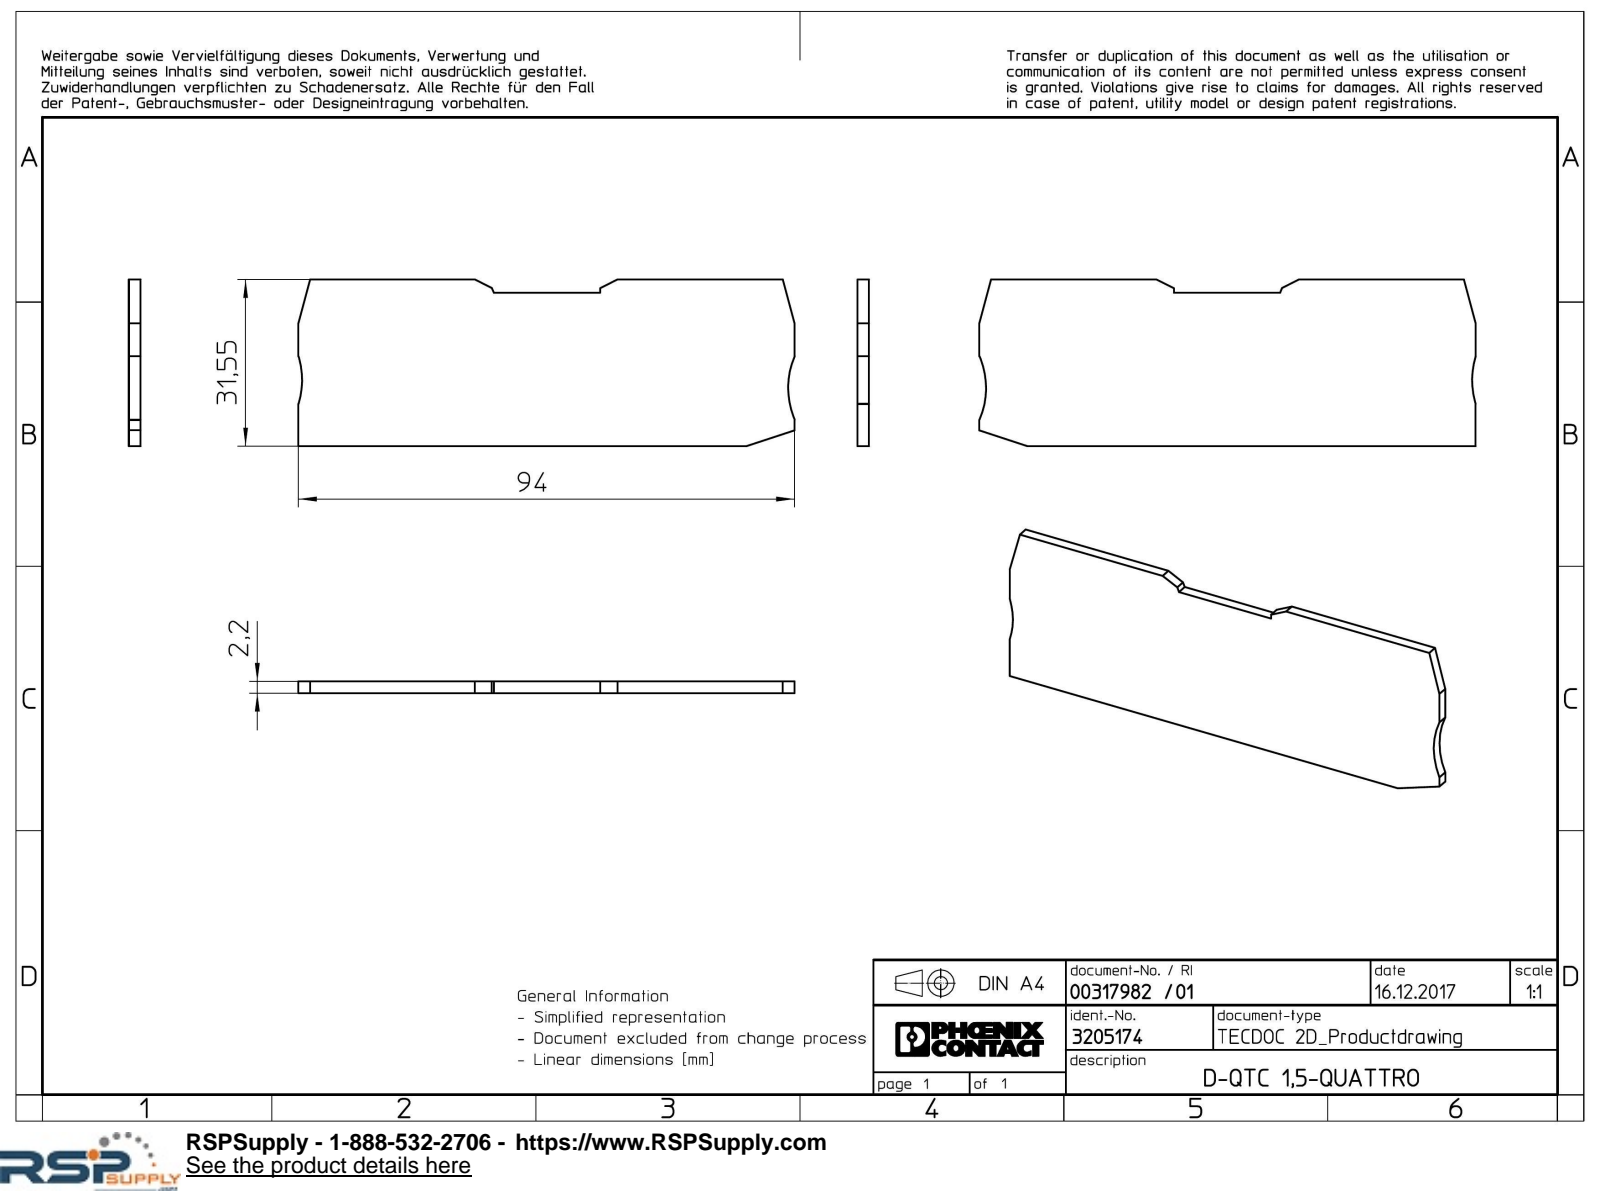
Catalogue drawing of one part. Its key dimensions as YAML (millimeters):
part_name: "D-QTC_1.5-QUATTRO-select"
step_written_by: "Creo Elements/Direct Modeling 18.1I 14-Aug-2016 (C) Parametric Technology GmbH (AUTOMOTIVE_DESIGN)"
units: millimeters
bodies: {solids: 1, faces: 19, planar: 17, cylindrical: 2, other: 0}
overall_size: [94, 31.55, 2.2]
volume: 6298
surface_area: 6270
partial_cylinders:
  - {radius: 15, count: 2}
face_to_face_distances: [2.2, 31.55, 29.05, 2.5, 94, 57.15, 36.85]
